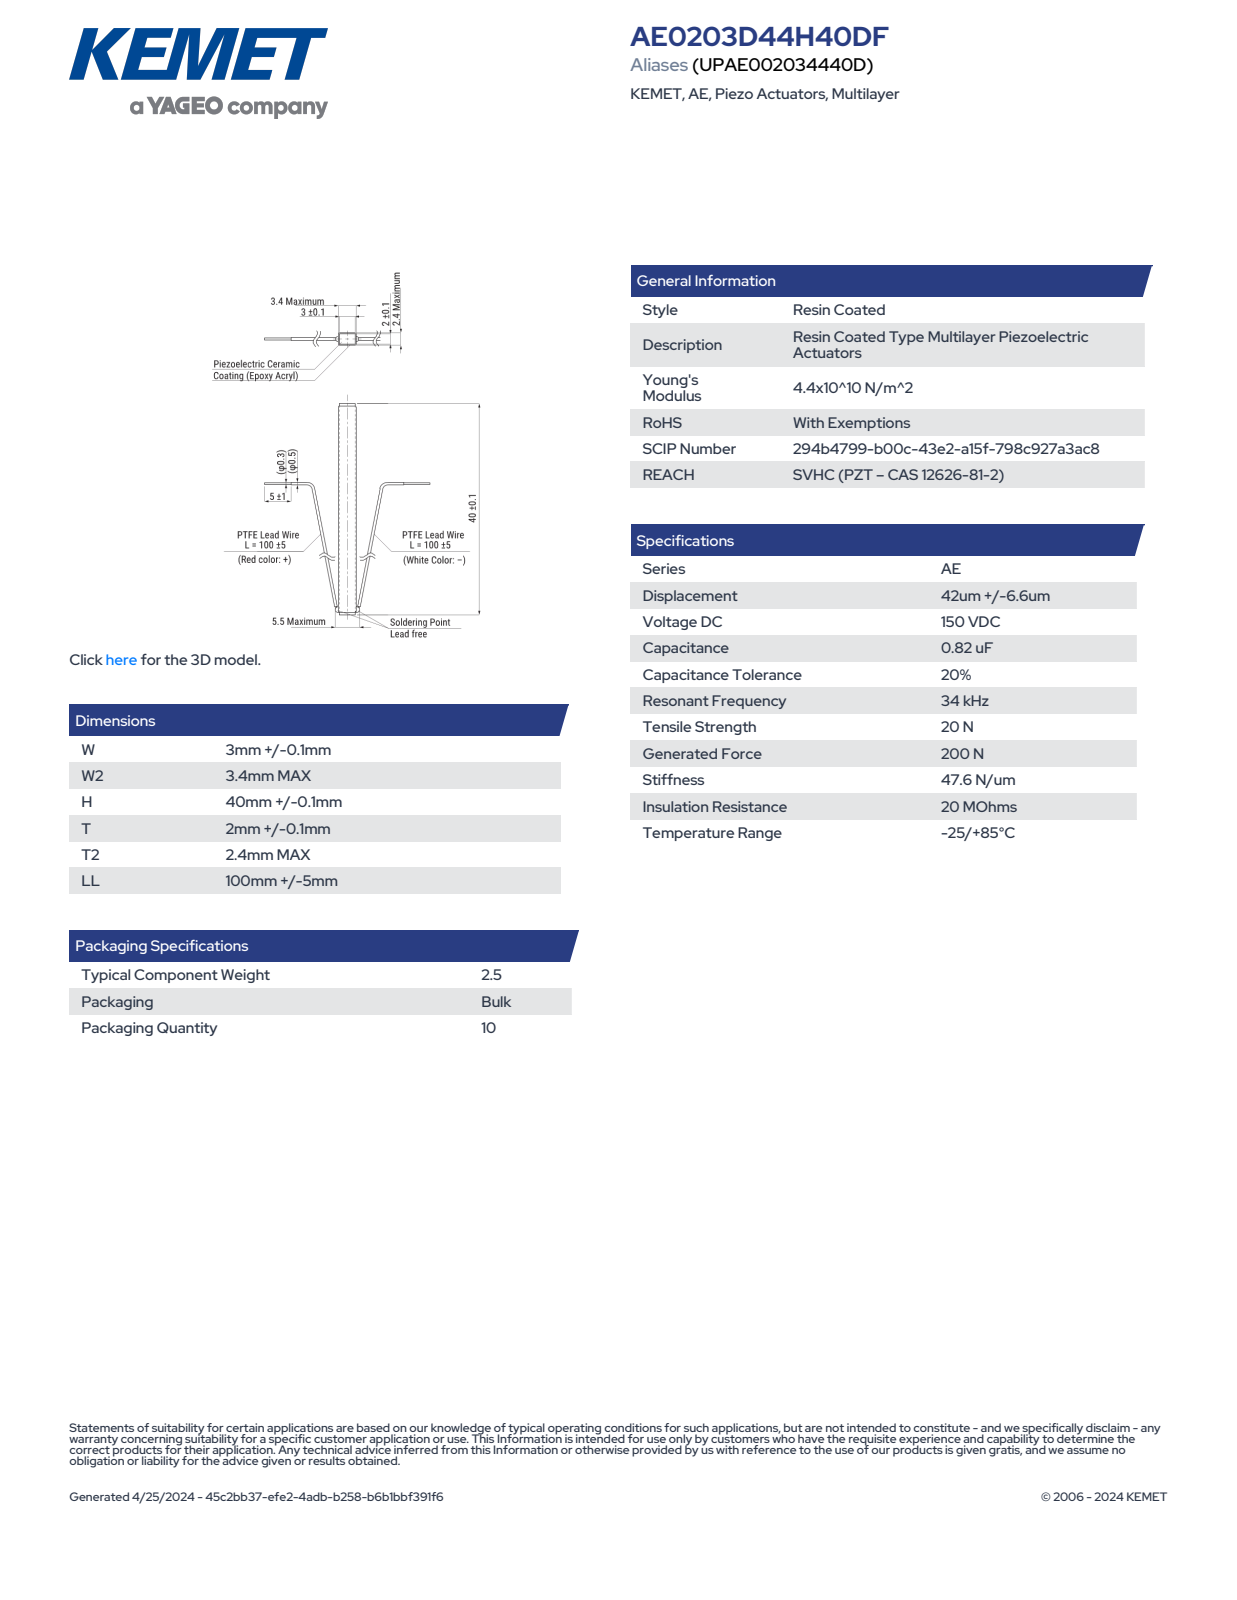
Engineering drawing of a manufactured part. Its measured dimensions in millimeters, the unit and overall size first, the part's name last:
Units: millimetres
Overall size (bounding box): 40.1 × 3.4 × 2.4
Partial cylindrical surfaces — rounded edges, fillets, slot ends (radius × count): R0.15 ×8
Main face-to-face distances: 2.25, 3, 2.1, 2.9, 2.4, 3.1, 40.1, 16.12, 23.98, 3.93
Volume: 265 mm³ · Surface area: 438 mm²
Bodies: 4 solids, 93 faces (85 planar, 8 cylindrical, 0 other)
Part name (STEP PRODUCT): AL_KAE2_W3.1W23.4H40.1T2.1T22.4
STEP written by: SolidWorks 2020 (AUTOMOTIVE_DESIGN)
